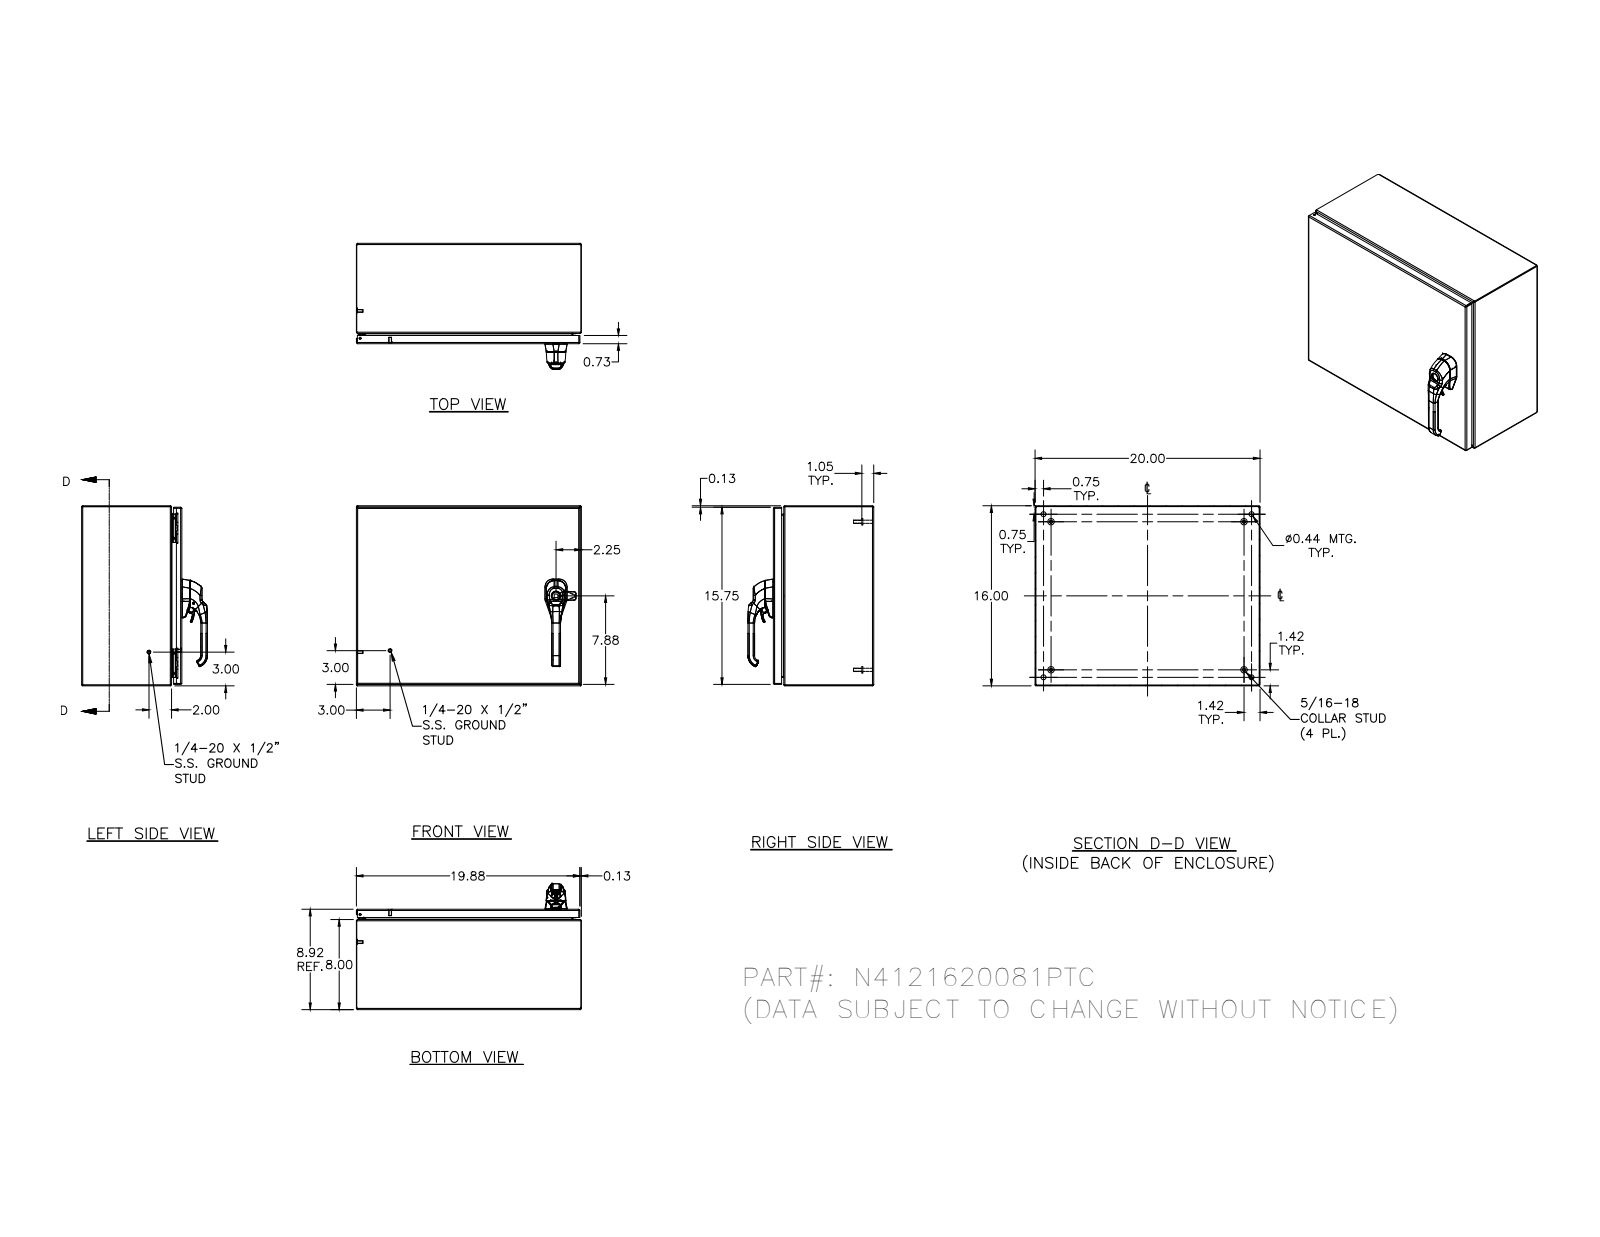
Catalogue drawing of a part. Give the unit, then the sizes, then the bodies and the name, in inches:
Units: inches
Overall size (bounding box): 20 × 16 × 11.095
Round holes (diameter × count): ⌀0.188 ×5, ⌀0.093 ×4, ⌀0.152 ×4, ⌀0.167 ×4, ⌀0.172 ×4, ⌀0.437 ×4, ⌀0.28 ×3, ⌀0.156 ×2, ⌀0.187 ×1
Round bosses / shafts (diameter × count): ⌀0.25 ×10, ⌀0.563 ×4, ⌀0.36 ×4, ⌀0.32 ×4, ⌀0.3 ×4, ⌀0.275 ×4, ⌀0.256 ×4, ⌀0.164 ×4
Partial cylindrical surfaces — rounded edges, fillets, slot ends (radius × count): R0.031 ×30, R0.05 ×26, R0.105 ×20, R0.016 ×18, R0.125 ×14, R0.032 ×8, R0.067 ×8, R0.068 ×8
Main face-to-face distances: 0.074, 8.843, 8.917, 15.926, 8.769, 19.926, 16, 15.852, 20, 19.852
Hole centre spacings: 11.996, 18.872, 0.017, 0.66, 12.656, 0.019, 0.5, 0.648
Volume: 110.4 in³ · Surface area: 2 778 in²
Bodies: 28 solids, 1280 faces (417 planar, 474 cylindrical, 389 other)
Part name (STEP PRODUCT): N4121620081PTC
STEP written by: SolidWorks 2018 (AUTOMOTIVE_DESIGN)
